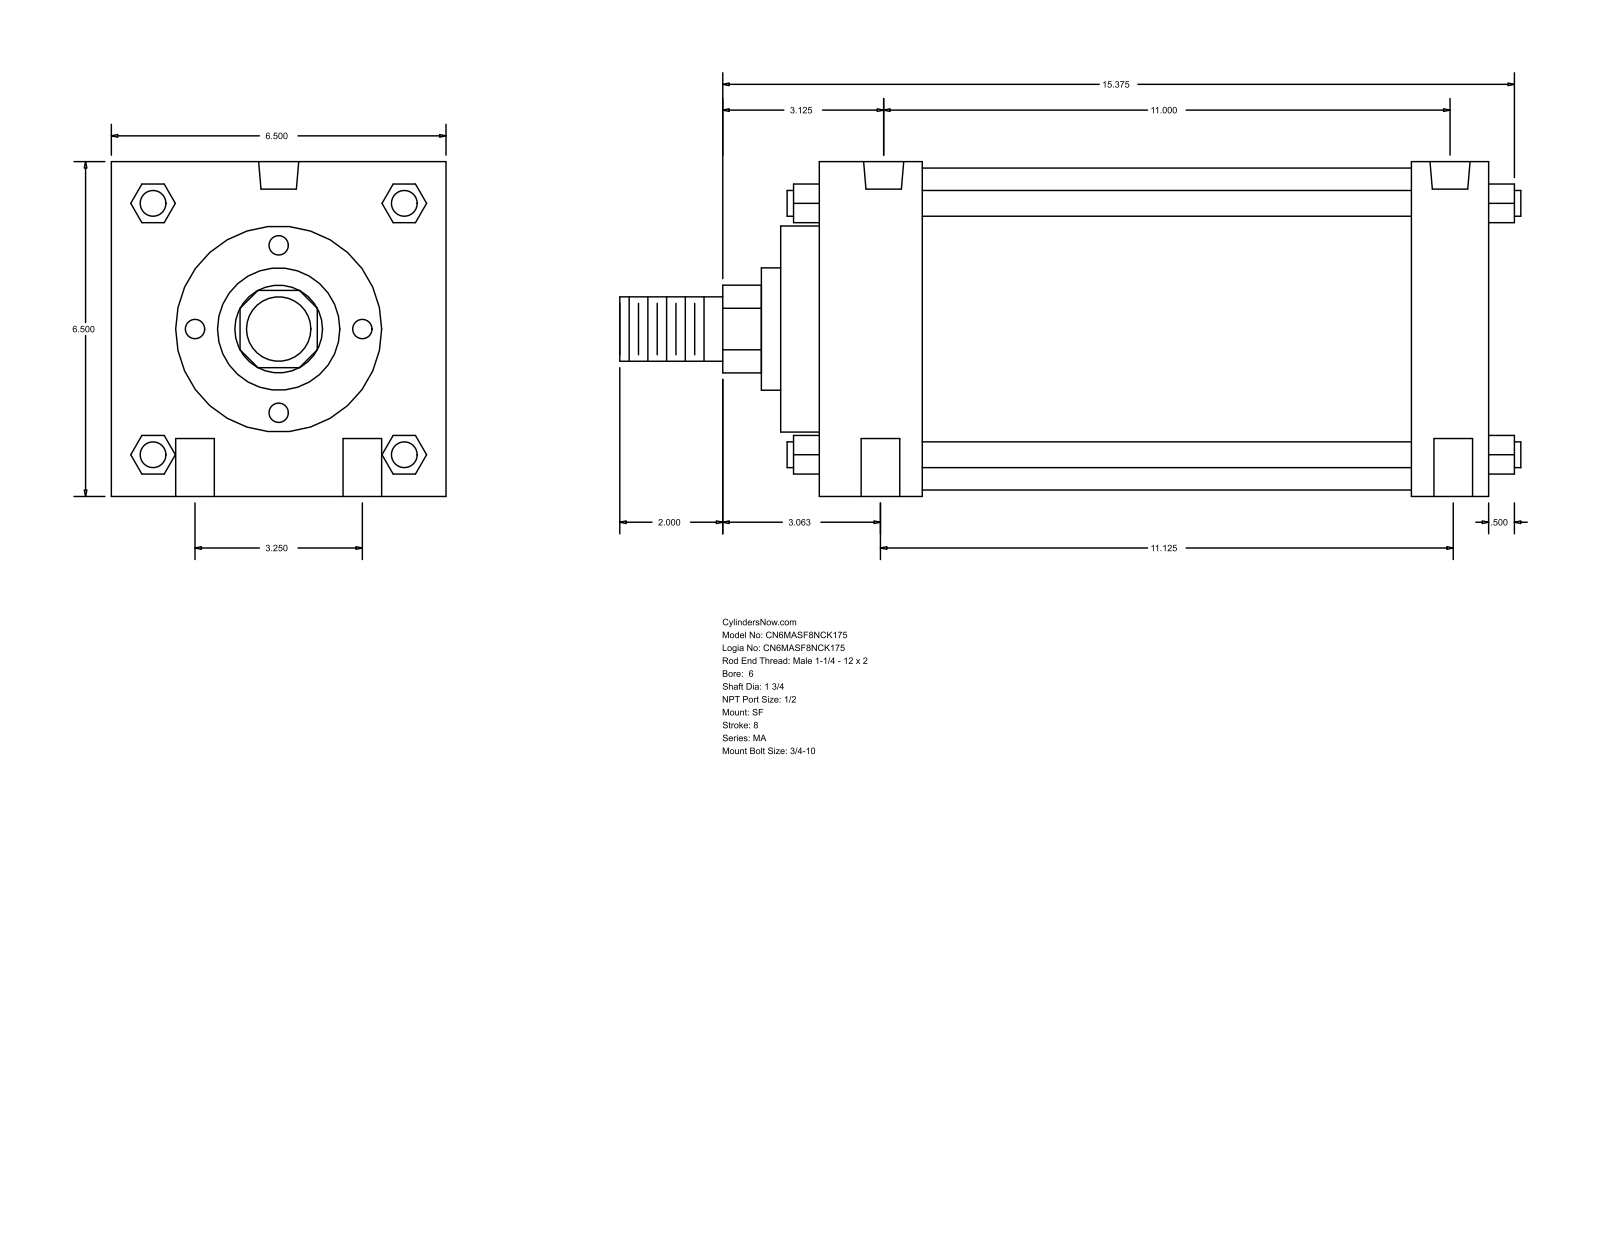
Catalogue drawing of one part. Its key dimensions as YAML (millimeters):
part_name: "MA_SF__0600_1.75"
step_written_by: "GSSL Pune (CONFIG_CONTROL_DESIGN)"
units: millimeters
bodies: {solids: 0, faces: 126, planar: 95, cylindrical: 31, other: 0}
overall_size: [444.5, 165.1, 165.1]
round_holes:
  - {diameter: 19.05, count: 4}
  - {diameter: 17.46, count: 2}
  - {diameter: 19.77, count: 2}
round_bosses_or_shafts:
  - {diameter: 12.7, count: 4}
  - {diameter: 158.75, count: 1}
  - {diameter: 101.6, count: 1}
  - {diameter: 60.33, count: 1}
  - {diameter: 44.45, count: 1}
  - {diameter: 31.75, count: 1}
partial_cylinders:
  - {radius: 21.63, count: 1}
face_to_face_distances: [165.1, 330.2, 19.05, 50.8, 292.11, 38.09, 241.31, 279.4, 69.85, 311.16]
hole_center_spacings: [41.3, 283.99, 82.54, 279.39, 282.57, 294.38]
